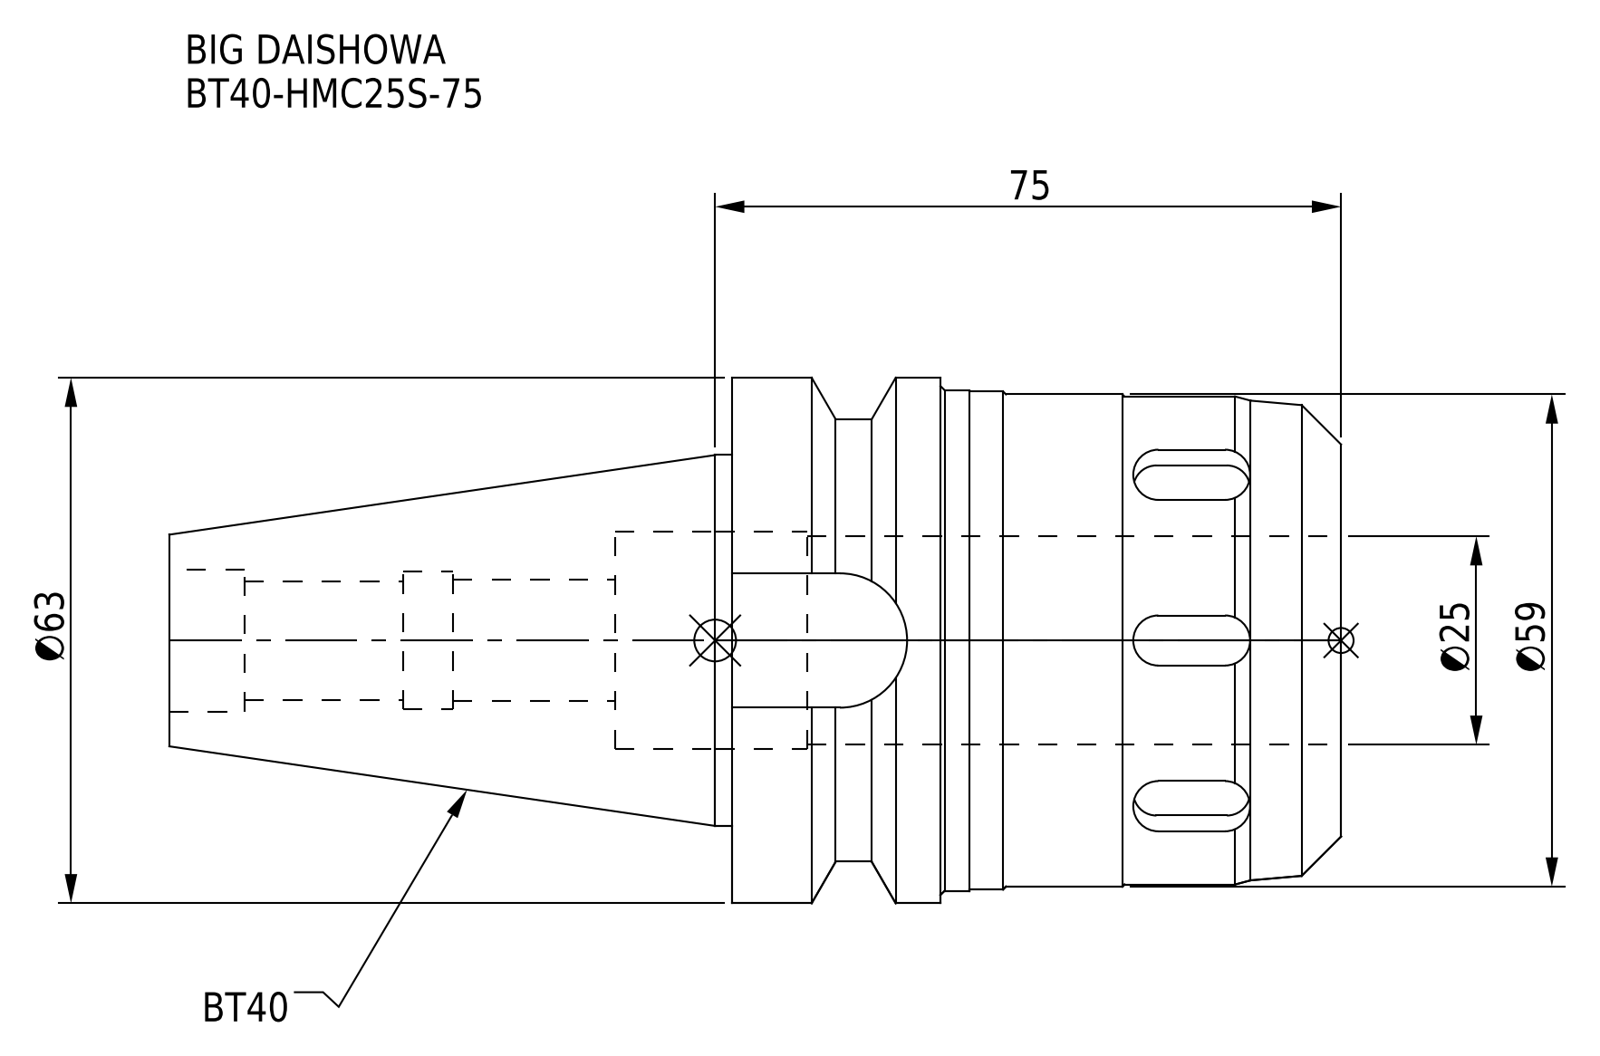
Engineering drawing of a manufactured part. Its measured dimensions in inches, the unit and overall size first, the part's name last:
Units: inches
Overall size (bounding box): 5.528 × 2.48 × 2.48
Round holes (diameter × count): ⌀0.559 ×1, ⌀0.571 ×1, ⌀0.65 ×1, ⌀0.669 ×1, ⌀0.984 ×1, ⌀1.024 ×1
Round bosses / shafts (diameter × count): ⌀2.48 ×1, ⌀2.362 ×1, ⌀2.35 ×1, ⌀2.323 ×1, ⌀2.303 ×1, ⌀2.087 ×1, ⌀1.75 ×1
Partial cylindrical surfaces — rounded edges, fillets, slot ends (radius × count): R0.118 ×12, R0.317 ×1
Main face-to-face distances: 2.874, 3.425, 0.551, 2.654, 1.772, 2.126, 5.528, 2.102, 1.181, 0.945
Volume: 12.62 in³ · Surface area: 56.71 in²
Bodies: 1 solid, 104 faces (40 planar, 46 cylindrical, 18 other)
Part name (STEP PRODUCT): BT40-HMC25S-75
STEP written by: CREO PARAMETRIC BY PTC INC, 2016380 (AUTOMOTIVE_DESIGN)
